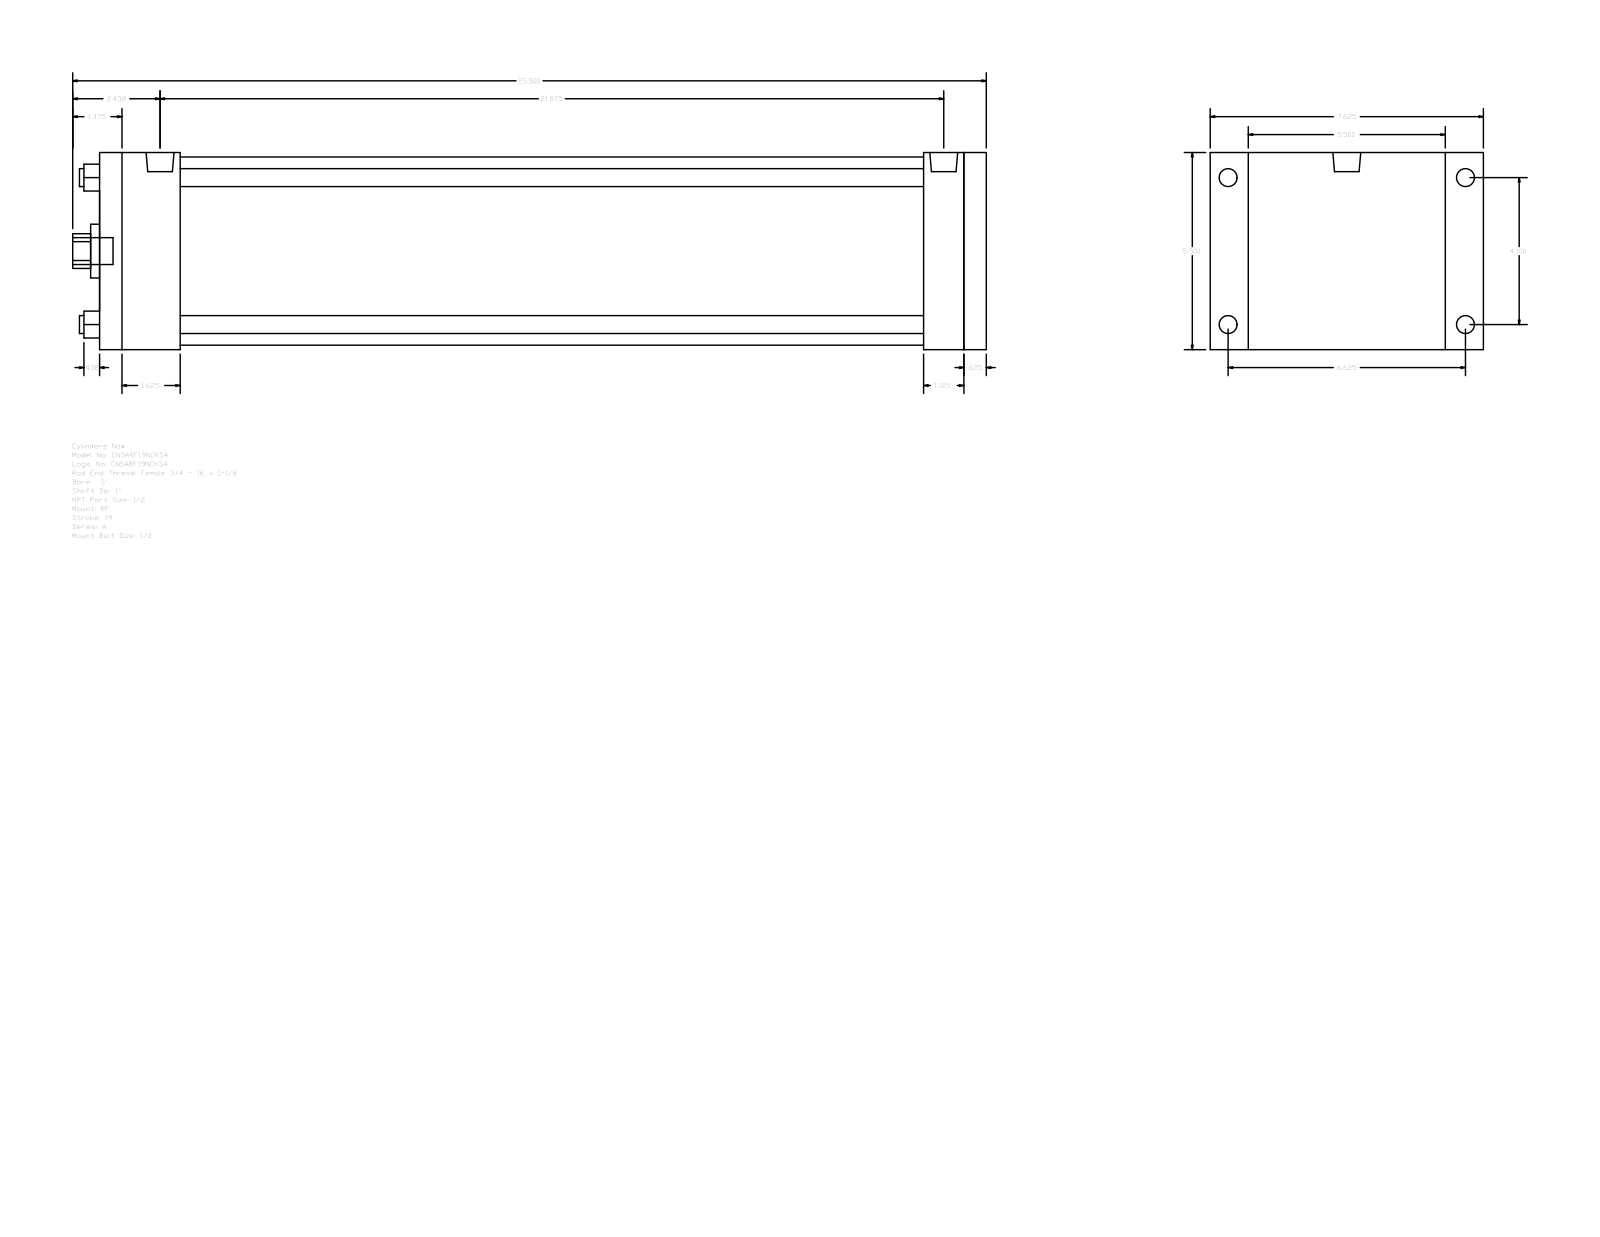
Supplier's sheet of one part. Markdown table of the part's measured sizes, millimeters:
| quantity | value |
| --- | --- |
| part name | A_RF__0500_1 |
| STEP written by | GSSL Pune (CONFIG_CONTROL_DESIGN) |
| units | millimeters |
| bodies | 0 solids, 92 faces (64 planar, 28 cylindrical, 0 other) |
| overall size | 647.7 × 193.68 × 139.7 |
| round holes (diameter × count) | 12.7 × 4, 25.4 × 1, 38.1 × 1, 133.35 × 1 |
| round bosses / shafts (diameter × count) | 12.7 × 4, 8.73 × 4, 19.77 × 2, 19.05 × 1 |
| partial cylindrical surfaces (radius × count) | 12.29 × 1 |
| main face-to-face distances | 139.7, 628.65, 15.87, 612.78, 57.15, 555.63, 571.5, 584.2, 527.05, 28.58 |
| hole center spacings | 73.64, 104.14, 147.28 |
